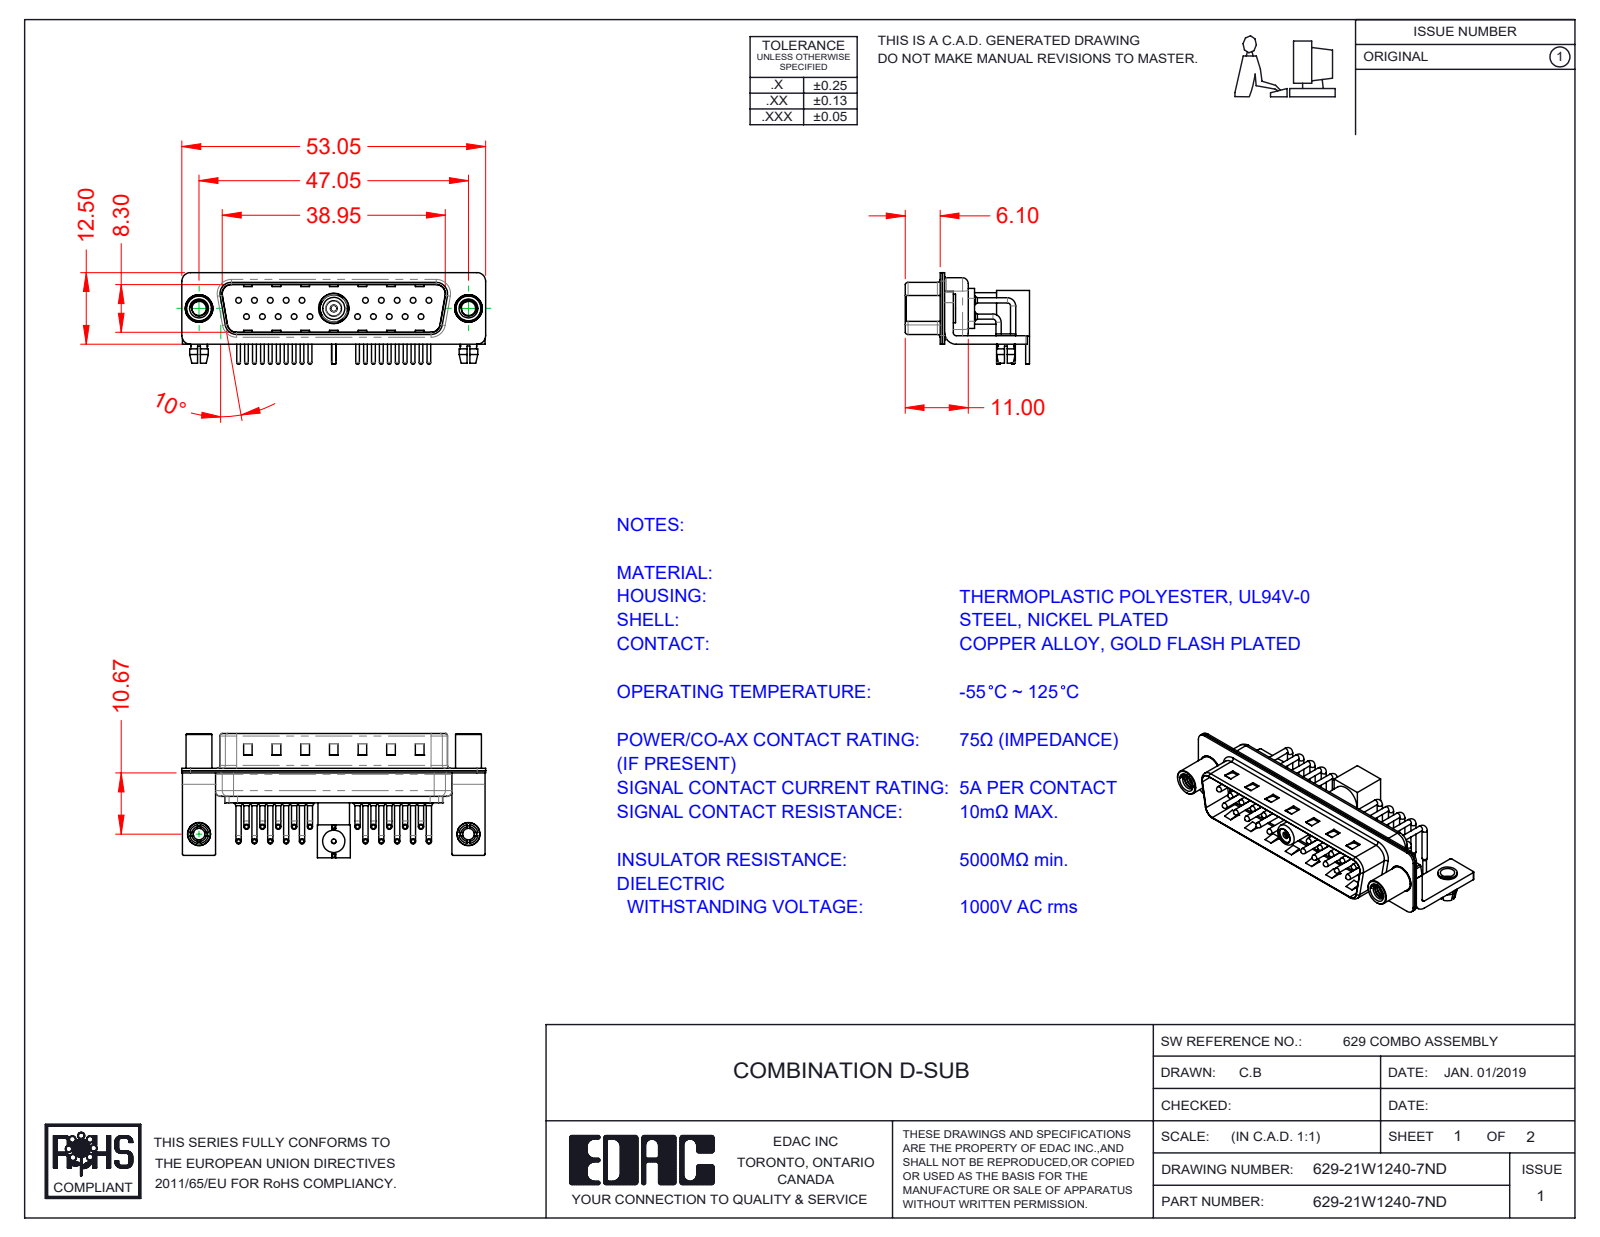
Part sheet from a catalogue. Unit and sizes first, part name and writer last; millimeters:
Units: millimetres
Overall size (bounding box): 53.05 × 21.71 × 16
Round holes (diameter × count): ⌀2 ×22, ⌀1.6 ×21, ⌀0.75 ×20, ⌀2.5 ×5, ⌀3.2 ×2, ⌀4 ×2, ⌀4.8 ×2, ⌀0.8 ×1, ⌀1.1 ×1, ⌀1.2 ×1, ⌀1.5 ×1, ⌀2.7 ×1
Round bosses / shafts (diameter × count): ⌀0.9 ×40, ⌀1.5 ×20, ⌀1 ×20, ⌀0.65 ×20, ⌀4 ×3, ⌀3.3 ×3, ⌀2.9 ×3, ⌀5 ×2
Partial cylindrical surfaces — rounded edges, fillets, slot ends (radius × count): R1.01 ×20, R0.25 ×16, R1.5 ×16, R2 ×13, R0.5 ×9, R1.6 ×8, R0.6 ×4, R0.65 ×4
Main face-to-face distances: 0.4, 0.8, 9.5, 9.1, 8.7, 1.5, 9.9, 0.6, 0.35, 2.1
Hole centre spacings: 3.16, 2.77, 5.54, 8.31, 5.04, 19.39, 20.97, 22.16
Volume: 3 586 mm³ · Surface area: 9 575 mm²
Bodies: 36 solids, 2918 faces (1578 planar, 1028 cylindrical, 312 other)
Part name (STEP PRODUCT): 629Combo Board Lock; 629Combo Contact Row 1; 629Combo Shell Rear_25 Contacts; 629Combo Threaded Standoff_D (+8 more)
STEP written by: SolidWorks 2020 (CONFIG_CONTROL_DESIGN)
